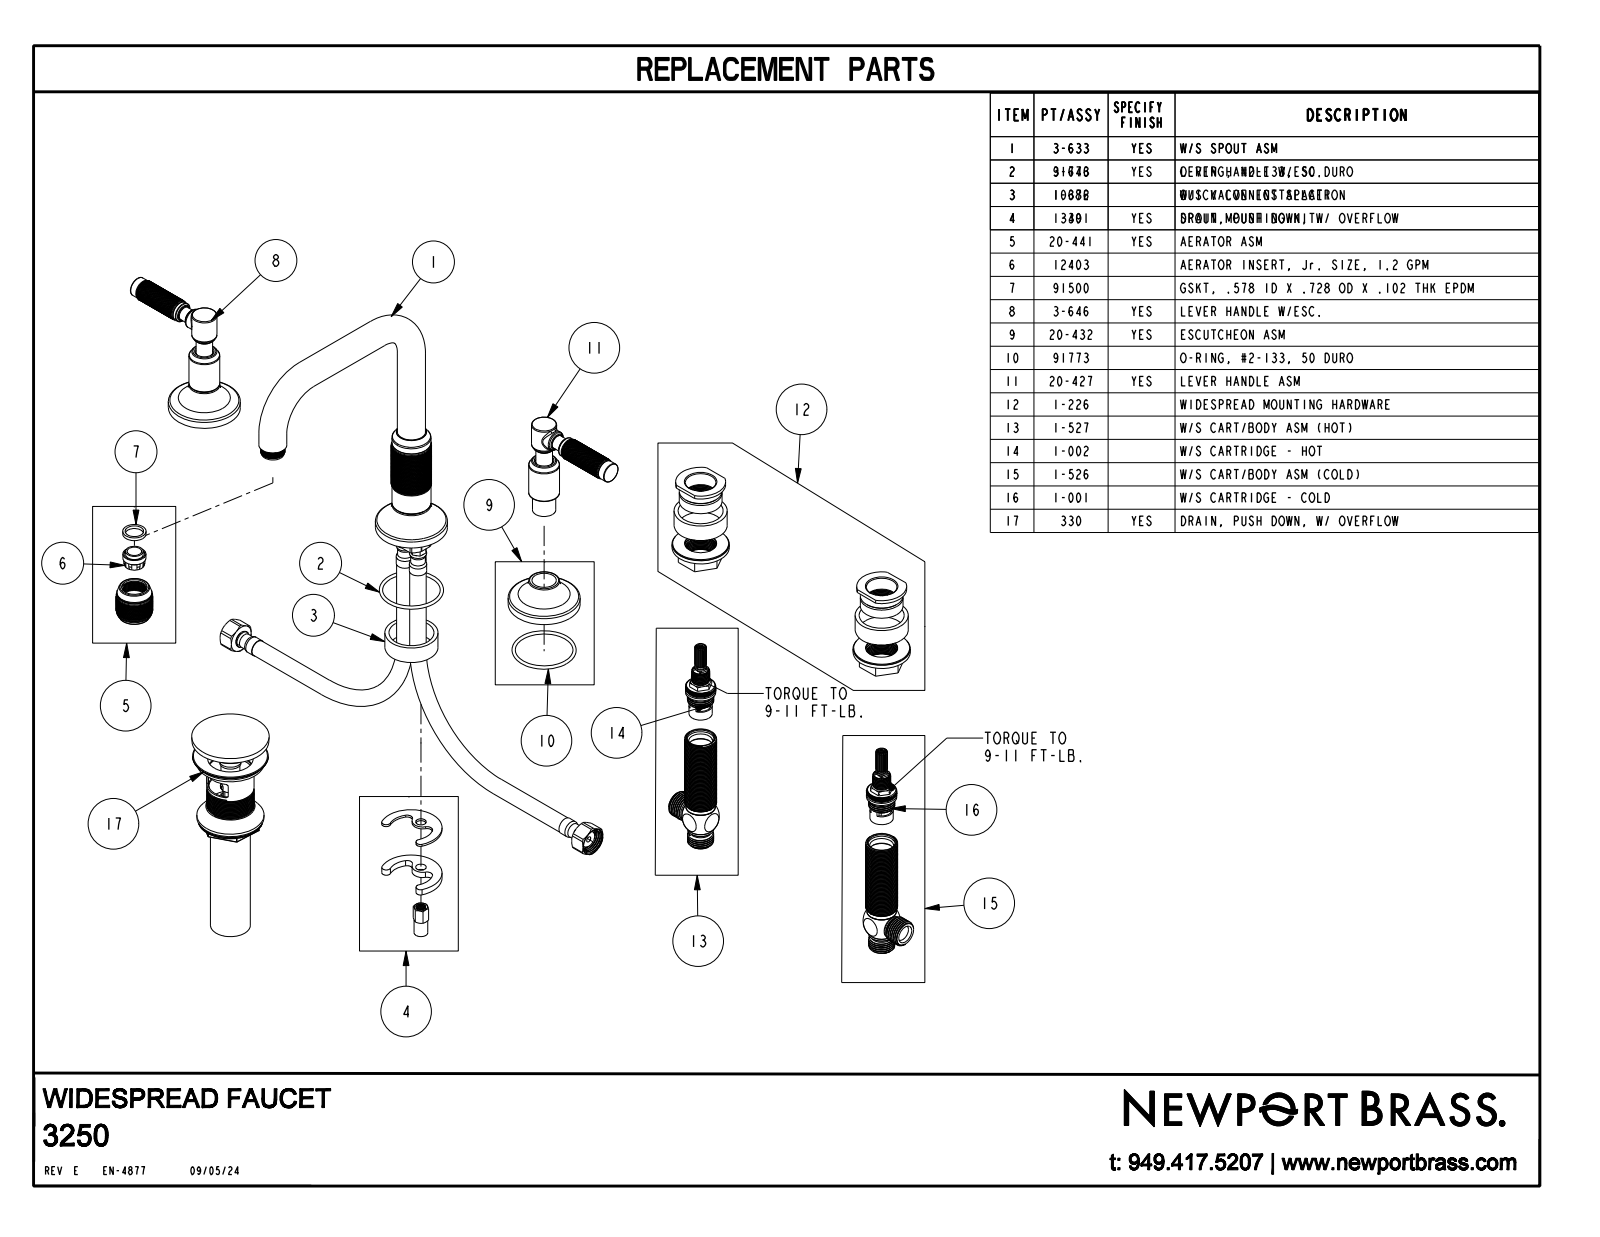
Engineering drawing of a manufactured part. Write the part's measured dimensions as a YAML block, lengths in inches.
part_name: "3250"
step_written_by: "CREO PARAMETRIC BY PTC INC, 2018400 (CONFIG_CONTROL_DESIGN)"
units: inches
bodies: {solids: 3, faces: 23976, planar: 20, cylindrical: 4642, other: 19314}
overall_size: [14.062, 8.597, 7.82]
volume: 21.64
surface_area: 110.9
round_holes:
  - {diameter: 0.47, count: 1}
round_bosses_or_shafts:
  - {diameter: 2.25, count: 3}
  - {diameter: 0.875, count: 3}
  - {diameter: 0.965, count: 2}
  - {diameter: 0.85, count: 2}
  - {diameter: 0.787, count: 2}
  - {diameter: 0.52, count: 2}
  - {diameter: 1.26, count: 1}
  - {diameter: 1.22, count: 1}
face_to_face_distances: [5.11, 2.158, 2.952, 0.9, 1.258, 4.21, 0.91, 1.248, 4.2, 3.65]
